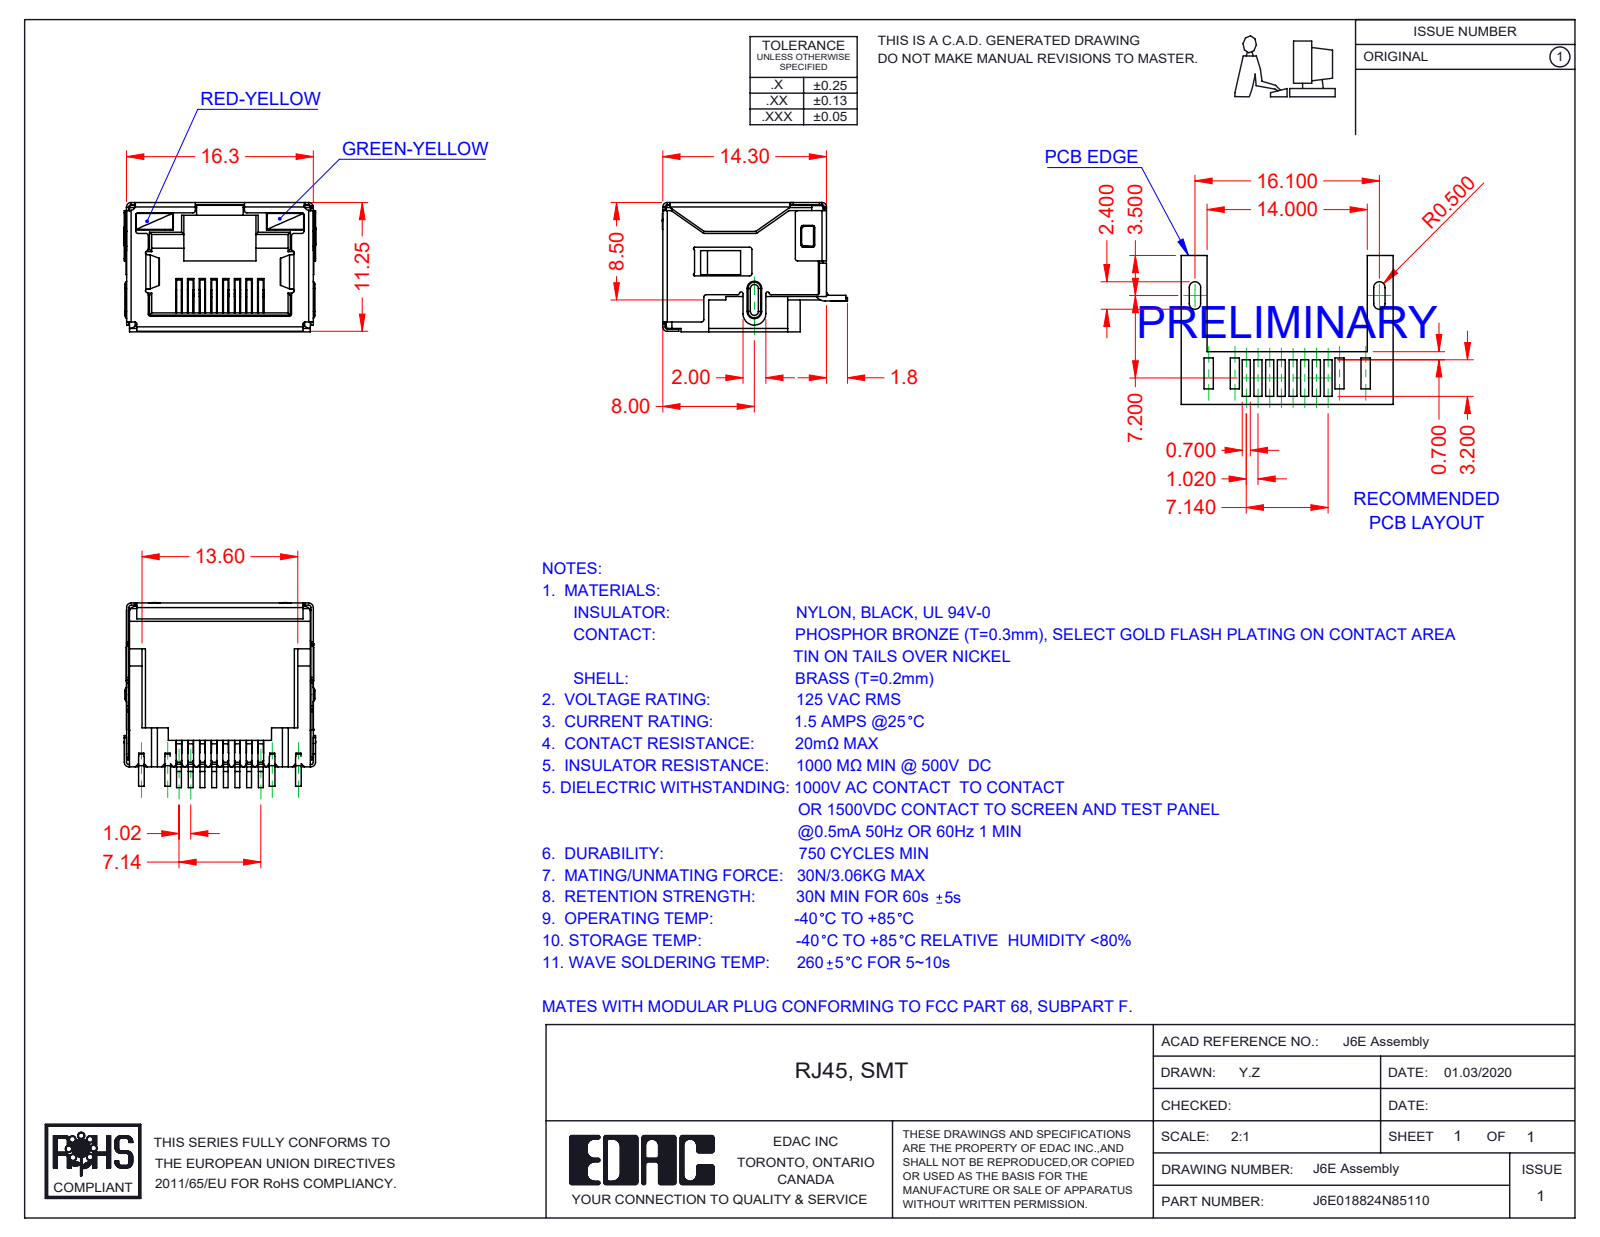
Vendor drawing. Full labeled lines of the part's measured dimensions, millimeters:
Part name (STEP PRODUCT): 6E LED LH_8-Red-Yellow; J6E018824N85110; 6E Contacts; 6E LED RH_5-Green-Yellow (+2 more)
STEP written by: SolidWorks 2016 (CONFIG_CONTROL_DESIGN)
Units: millimetres
Bodies: 12 solids, 1500 faces (1099 planar, 351 cylindrical, 50 other)
Overall size (bounding box): 16.75 × 16.15 × 11.3
Volume: 1 109 mm³ · Surface area: 4 045 mm²
Partial cylindrical surfaces — rounded edges, fillets, slot ends (radius × count): R0.2 ×82, R0.25 ×17, R0.4 ×13, R0.5 ×13, R0.1 ×10, R0.15 ×7, R0.3 ×4, R1 ×3
Main face-to-face distances: 11.05, 16.05, 16.1, 15.85, 11.1, 11.3, 2.4, 0.7, 9.85, 0.49
